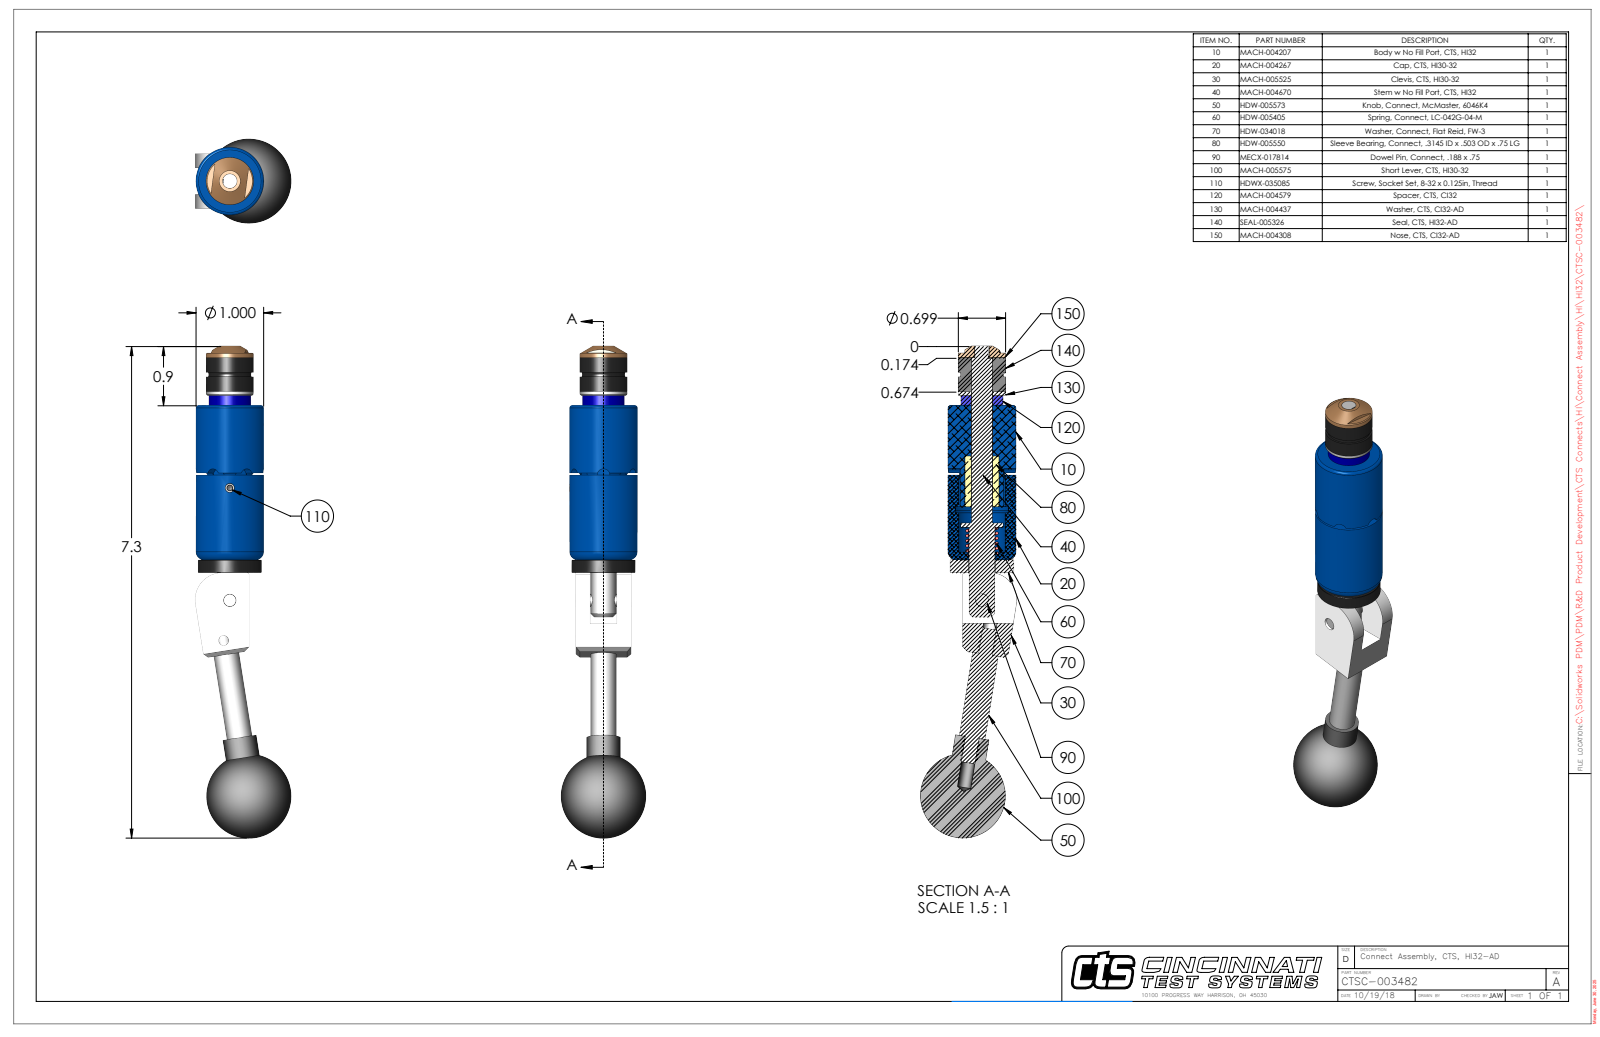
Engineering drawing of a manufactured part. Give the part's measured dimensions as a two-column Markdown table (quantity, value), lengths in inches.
| quantity | value |
| --- | --- |
| part name | CTSC-003482 |
| STEP written by | SolidWorks 2023 (AUTOMOTIVE_DESIGN) |
| units | inches |
| bodies | 10 solids, 253 faces (97 planar, 99 cylindrical, 57 other) |
| overall size | 7.268 × 1.416 × 1.25 |
| volume | 3.951 in³ |
| surface area | 33.55 in² |
| round holes (diameter × count) | 0.201 × 2, 0.136 × 1, 0.15 × 1, 0.189 × 1, 0.213 × 1, 0.31 × 1, 0.314 × 1, 0.316 × 1, 0.385 × 1, 0.392 × 1 |
| round bosses / shafts (diameter × count) | 0.25 × 2, 0.201 × 2, 1 × 1, 0.936 × 1, 0.699 × 1, 0.618 × 1, 0.5 × 1, 0.38 × 1 |
| partial cylindrical surfaces (radius × count) | 0.093 × 6, 0.029 × 2, 0.344 × 1, 0.4 × 1, 0.461 × 1 |
| main face-to-face distances | 0.21, 0.602, 2.283, 0.812, 2.47, 0.187, 0.702, 2.985, 3.172, 0.5 |
| hole center spacings | 0.599, 1.658, 2.252 |
